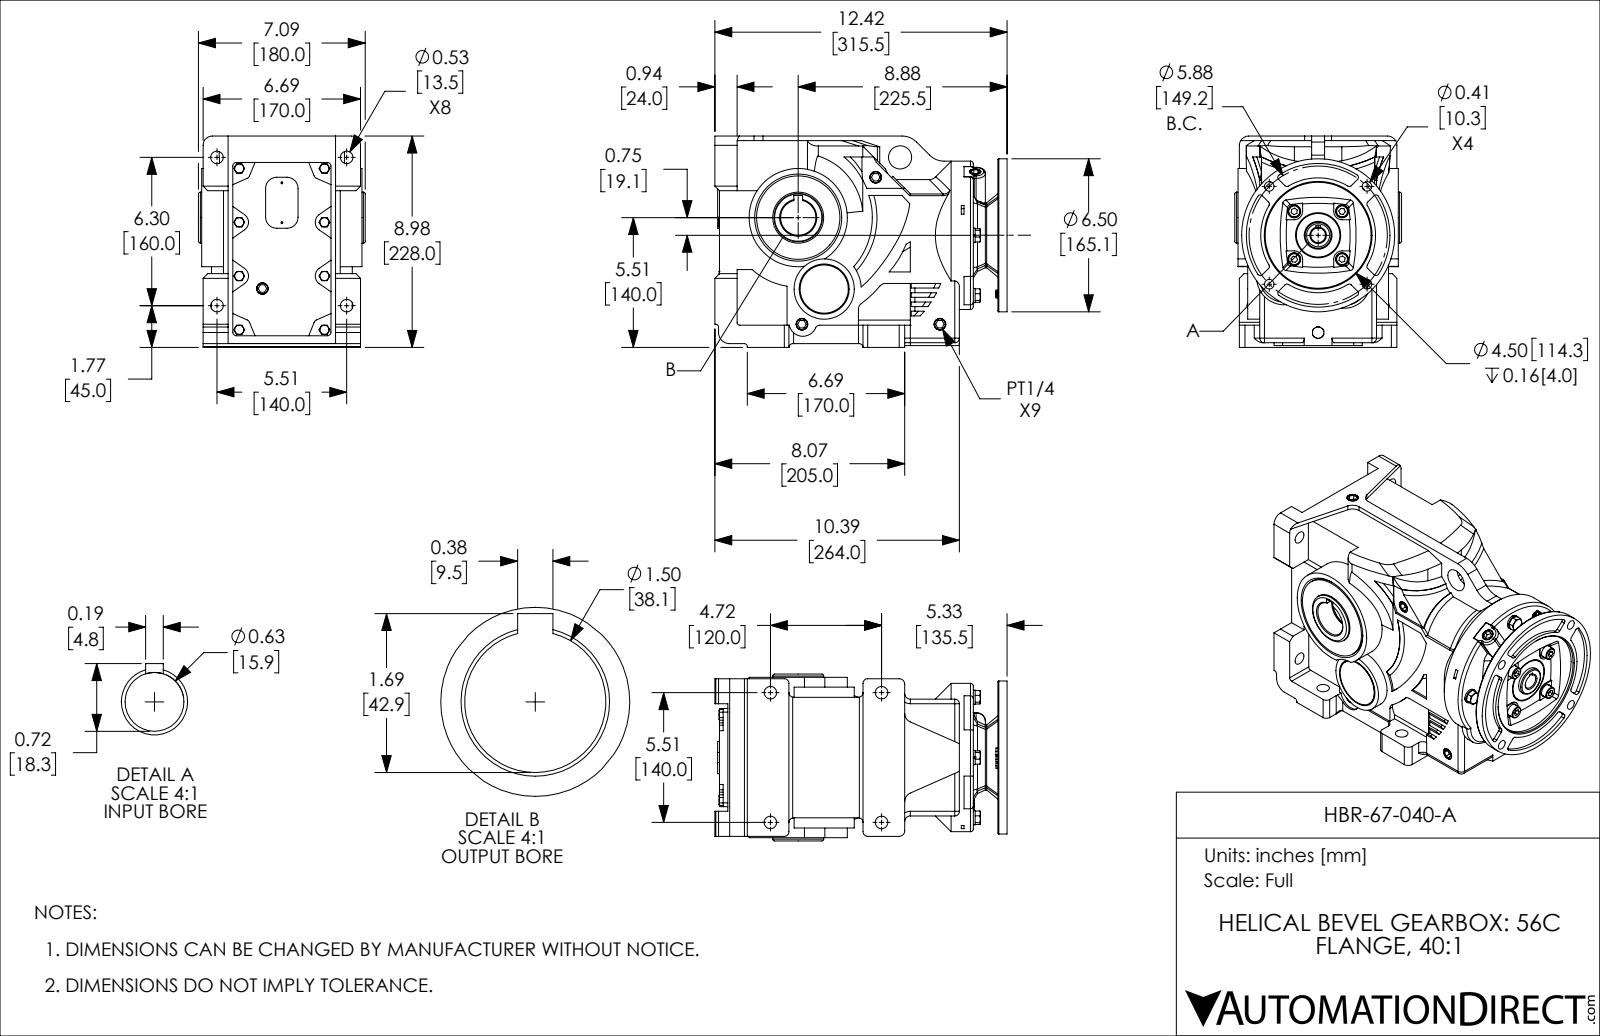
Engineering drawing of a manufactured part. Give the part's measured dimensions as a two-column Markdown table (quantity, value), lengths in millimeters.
| quantity | value |
| --- | --- |
| part name | HBR-67-040-A |
| STEP written by | SolidWorks 2018 (AUTOMOTIVE_DESIGN) |
| units | millimeters |
| bodies | 1 solid, 1106 faces (550 planar, 274 cylindrical, 282 other) |
| overall size | 315.5 × 228 × 180 |
| volume | 7 761 000 mm³ |
| surface area | 405 400 mm² |
| round holes (diameter × count) | 13.5 × 8, 8.2 × 4, 9 × 4, 10.3 × 4, 14 × 4, 2 × 2, 15.9 × 1, 21.5 × 1, 25 × 1, 38.1 × 1, 40 × 1, 114.3 × 1 |
| round bosses / shafts (diameter × count) | 15.4 × 4, 13 × 4, 8 × 4, 165.1 × 1, 160 × 1, 106 × 1, 90 × 1, 65 × 1 |
| partial cylindrical surfaces (radius × count) | 3 × 23, 5 × 20, 10 × 13, 2 × 9, 4 × 6, 12 × 5, 6 × 4, 9 × 4 |
| main face-to-face distances | 5, 2, 4, 24, 223, 1.5, 126, 300.5, 3, 15 |
| hole center spacings | 46.9, 54.2, 38.1, 65, 74.6, 83.1, 83.1, 91.9 |
